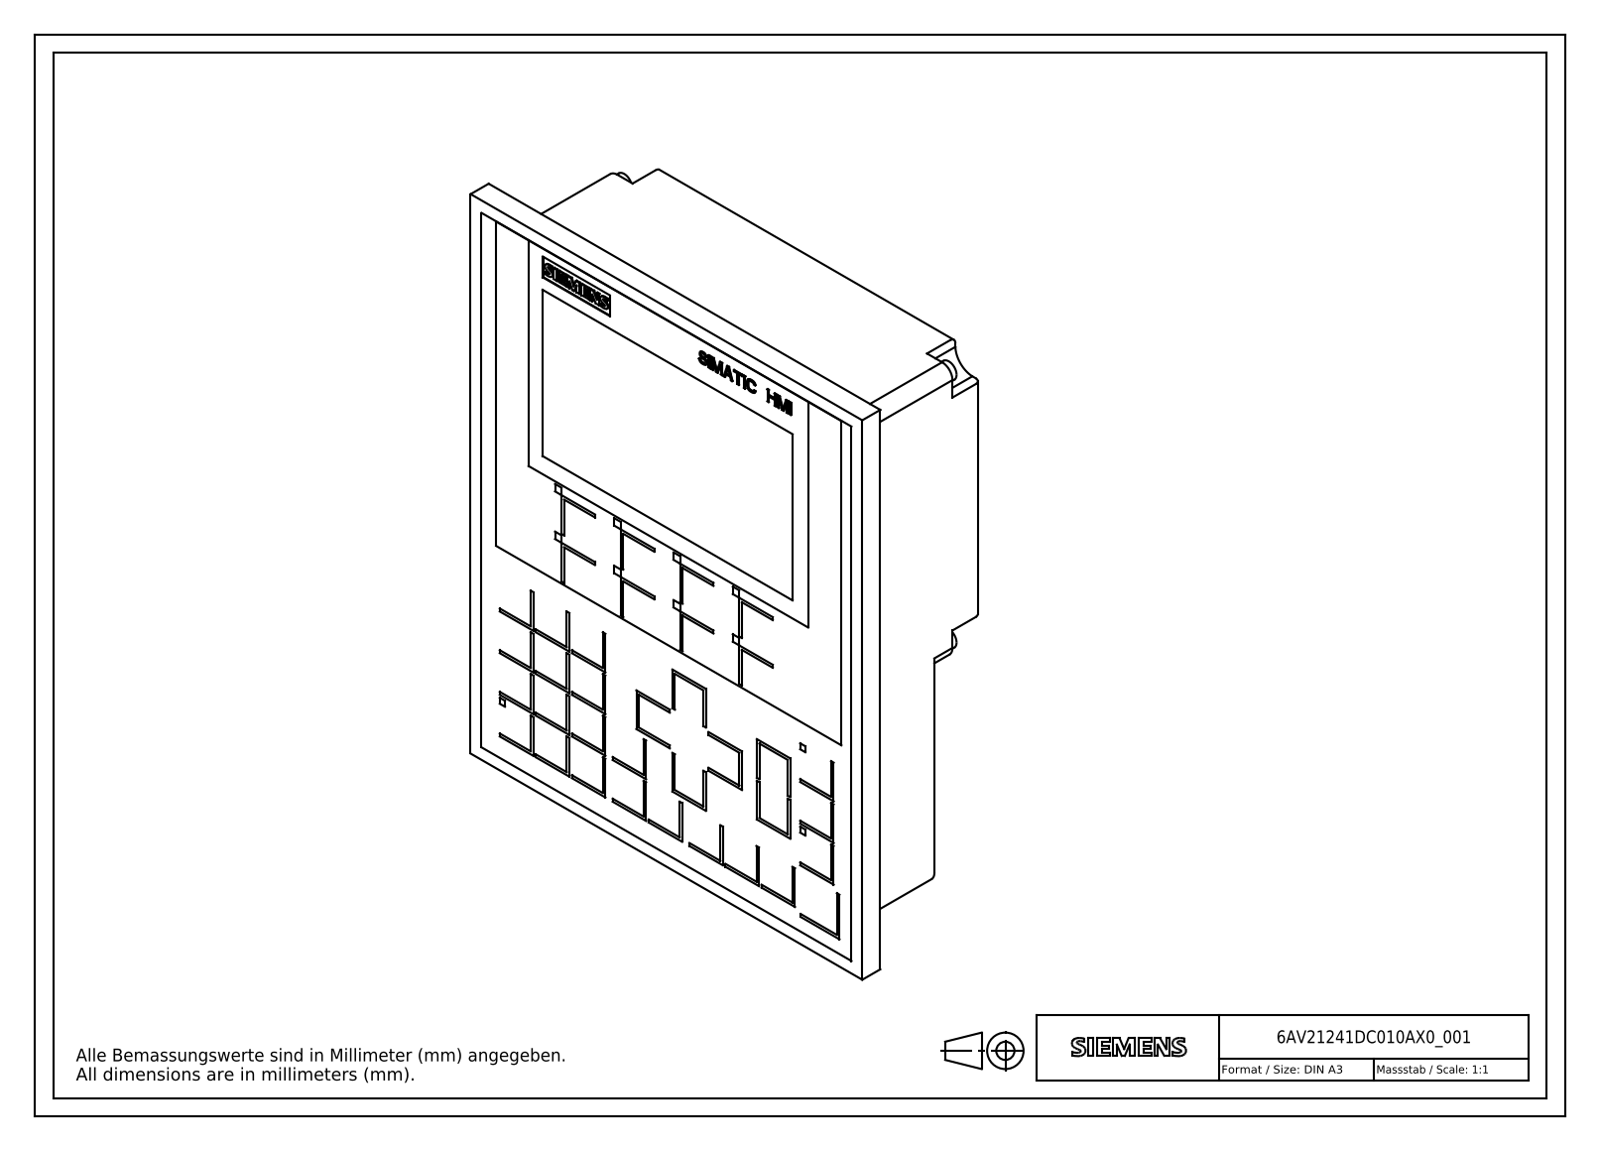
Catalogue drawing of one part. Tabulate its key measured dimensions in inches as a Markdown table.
| quantity | value |
| --- | --- |
| part name | A5E30292230A_001; A5E30291441A_001; A5E30291439A_001; A5E30291437A_001 |
| STEP written by | SIEMENS UGS NX 6.0 (AUTOMOTIVE_DESIGN) |
| units | inches |
| bodies | 249 solids, 2698 faces (2310 planar, 156 cylindrical, 232 other) |
| overall size | 7.402 × 5.984 × 2.169 |
| volume | 51.54 in³ |
| surface area | 286 in² |
| round holes (diameter × count) | 0.035 × 9, 0.094 × 2 |
| round bosses / shafts (diameter × count) | 0.236 × 4, 0.118 × 2, 0.038 × 2, 0.031 × 2, 0.315 × 1, 0.217 × 1 |
| partial cylindrical surfaces (radius × count) | 0.008 × 53, 0.004 × 10, 0.059 × 8, 0.033 × 6, 0.157 × 6, 0.018 × 4, 0.073 × 4, 0.079 × 4 |
| main face-to-face distances | 0.197, 0.264, 1.89, 2.154, 1.693, 0.461, 0.079, 0.354, 0.276, 0.262 |
| hole center spacings | 0.121, 0.109, 0.195, 0.217, 0.292, 0.326, 0.28, 0.333 |
